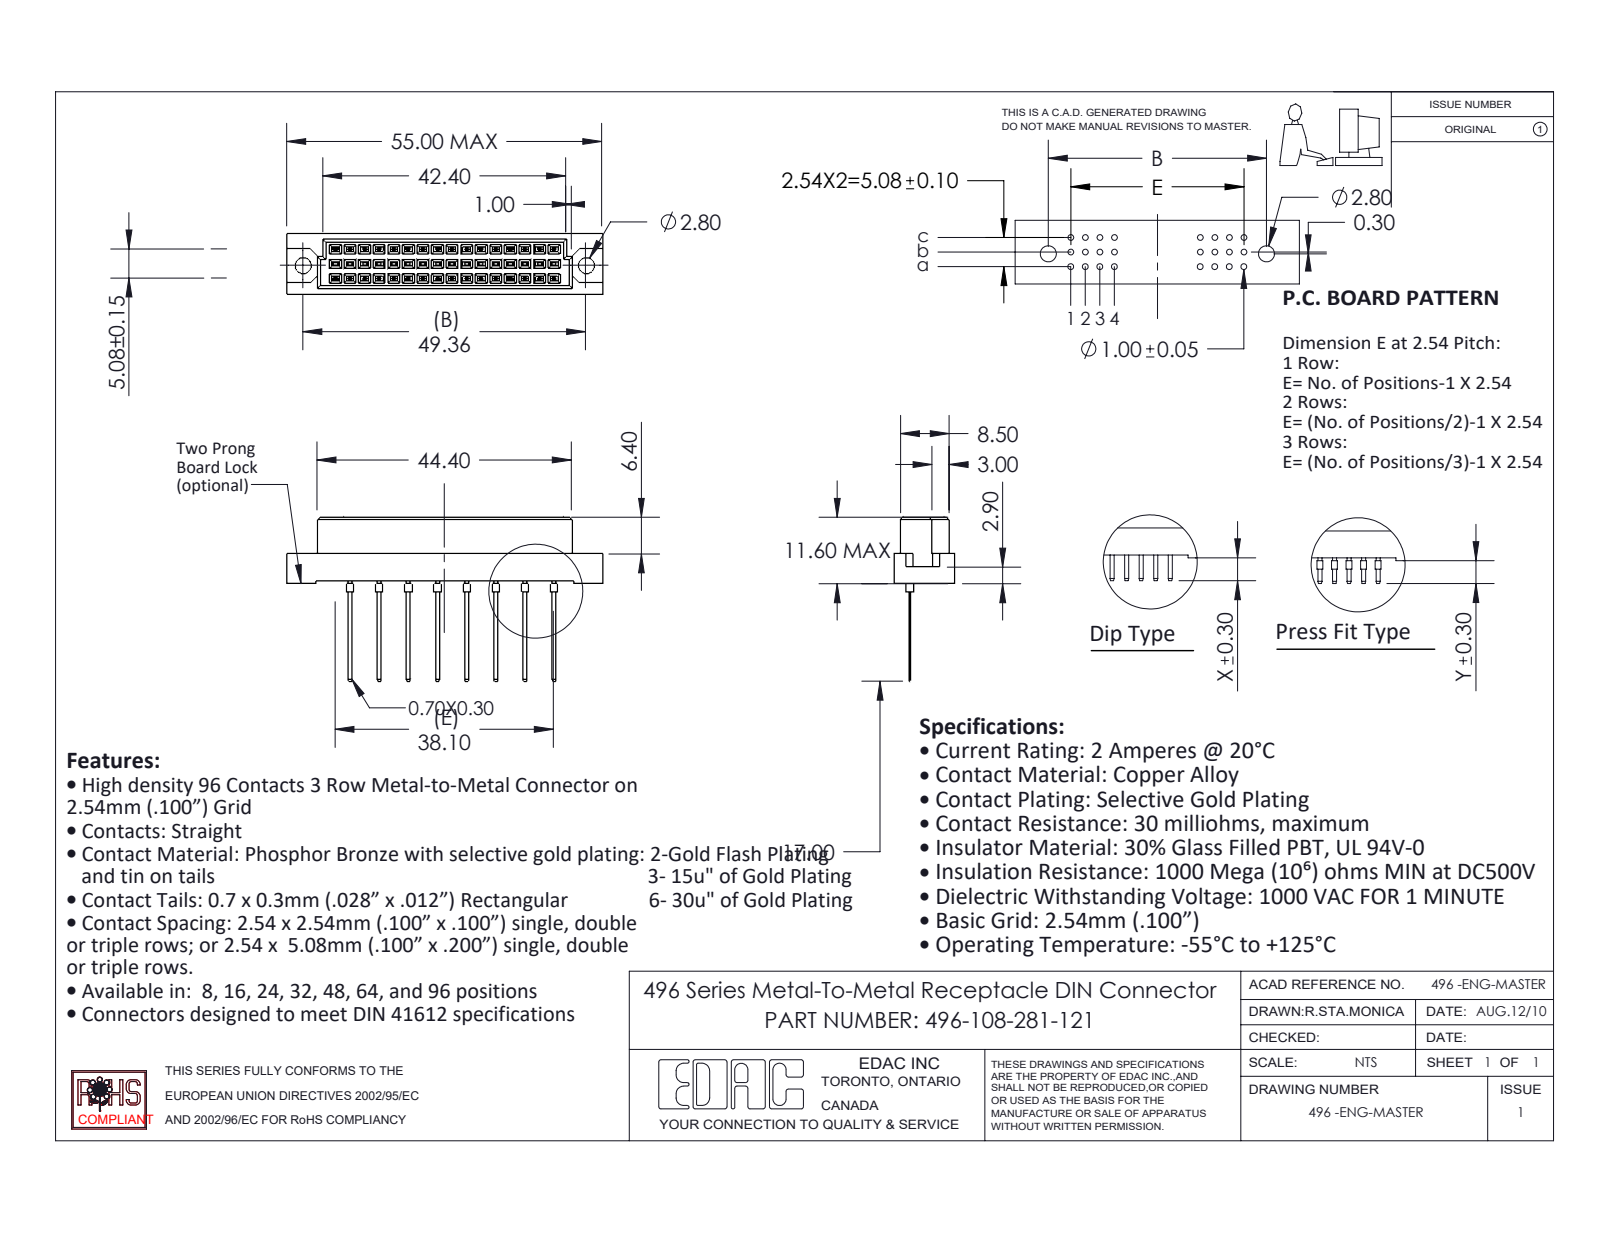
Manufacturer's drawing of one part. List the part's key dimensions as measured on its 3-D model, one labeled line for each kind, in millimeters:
Part name (STEP PRODUCT): 496 Part_48; 496-290_81; 496-108-281-121
STEP written by: SolidWorks 2020 (CONFIG_CONTROL_DESIGN)
Units: millimetres
Bodies: 9 solids, 810 faces (790 planar, 20 cylindrical, 0 other)
Overall size (bounding box): 55 × 28.6 × 10.6
Volume: 4 633 mm³ · Surface area: 4 588 mm²
Round holes (diameter × count): ⌀2.8 ×2
Round bosses / shafts (diameter × count): ⌀1 ×8
Main face-to-face distances: 2.54, 5.08, 1.05, 9.55, 0.81, 10.6, 3.35, 1.73, 8.5, 0.56
Hole centre spacings: 49.36
